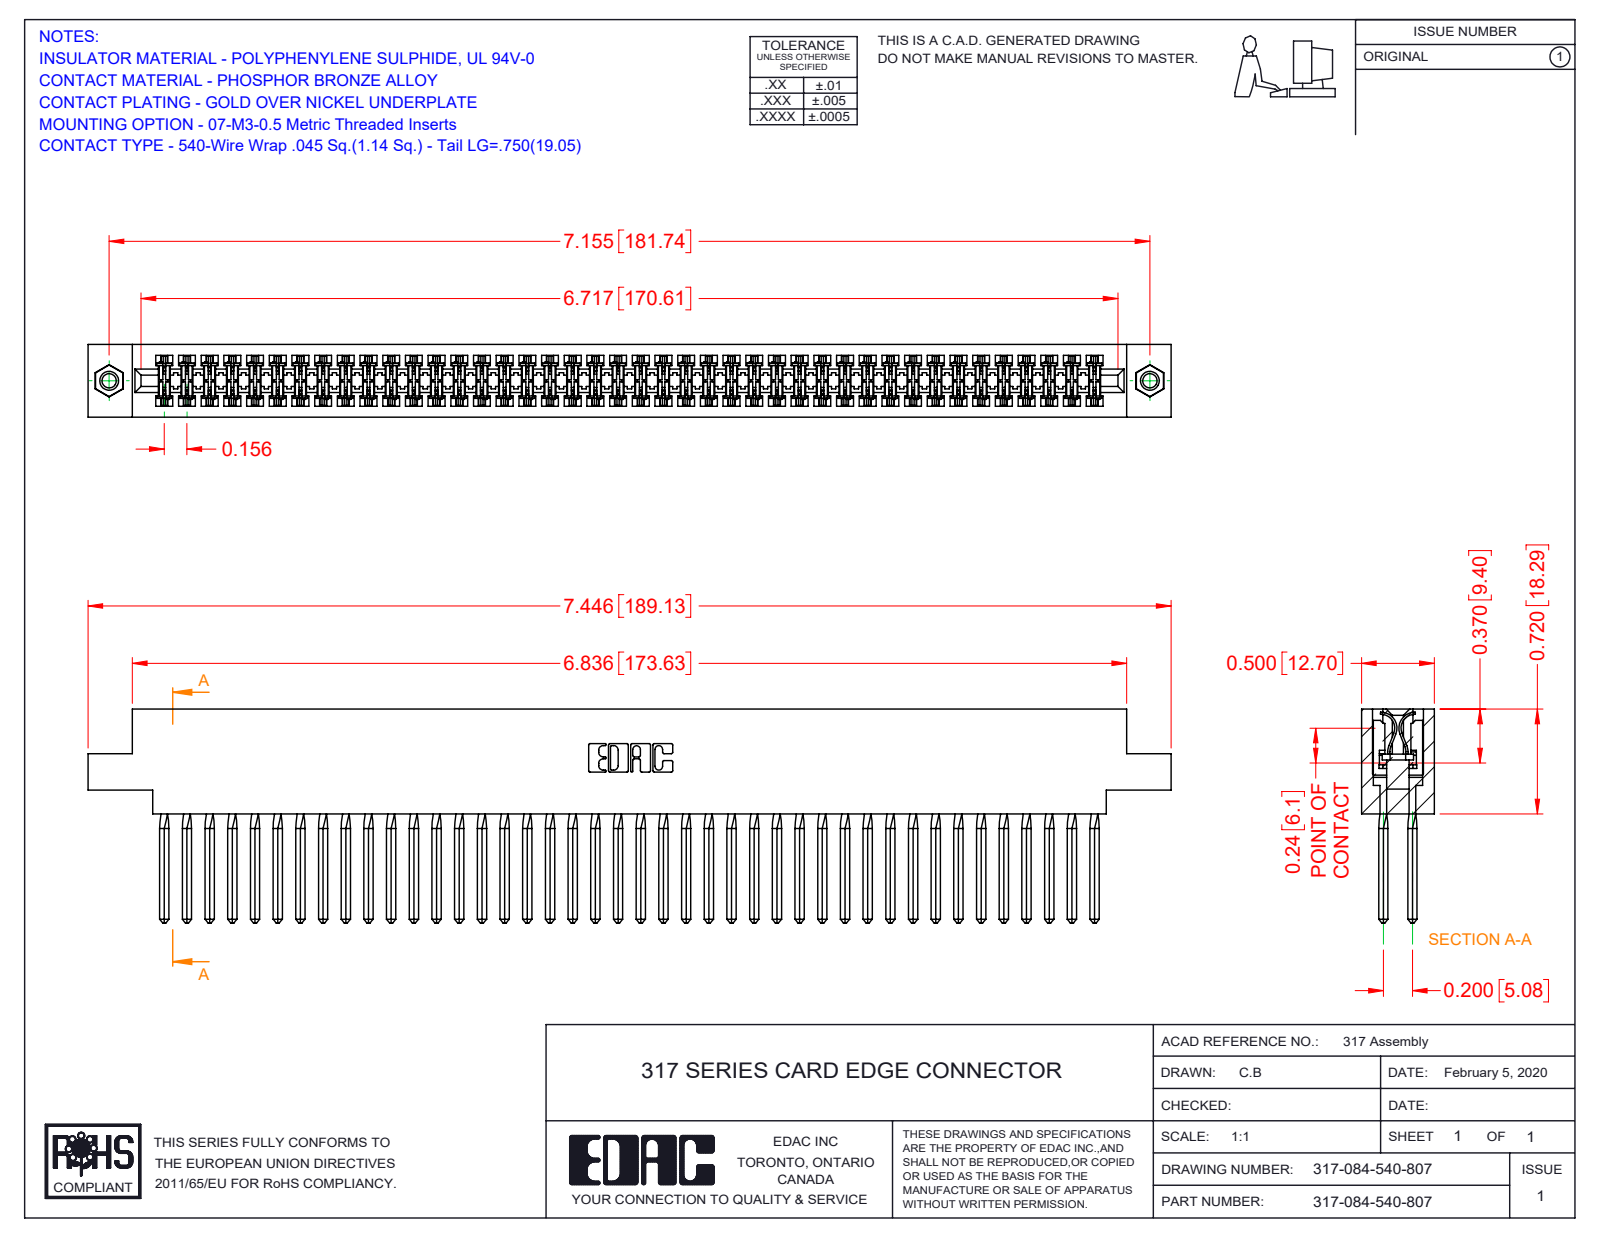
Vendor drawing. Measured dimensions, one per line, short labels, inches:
name: 317-290-001_540; 317 Part_.156 Dia - TI; 345-250-001_345-250-005-103; 317-084-540-807
written by: SolidWorks 2016 (CONFIG_CONTROL_DESIGN)
unit: in
bodies: 87 solids, 7638 faces (6222 planar, 1064 cylindrical, 352 other)
size: 7.446 × 1.47 × 0.5
volume: 1.936 in³; area: 73.38 in²
holes: 2× ⌀0.098, 2× ⌀0.125, 2× ⌀0.156
bosses: 2× ⌀0.155
rounds: 168× R0.015, 22× R0.01, 6× R0.007, 6× R0.031, 3× R0.026, 2× R0.095, 2× R0.1, 2× R0.11
face distances: 0.5, 0.075, 0.425, 0.35, 0.195, 0.094, 0.2, 0.115, 0.131, 0.046
hole spacings: 7.155
